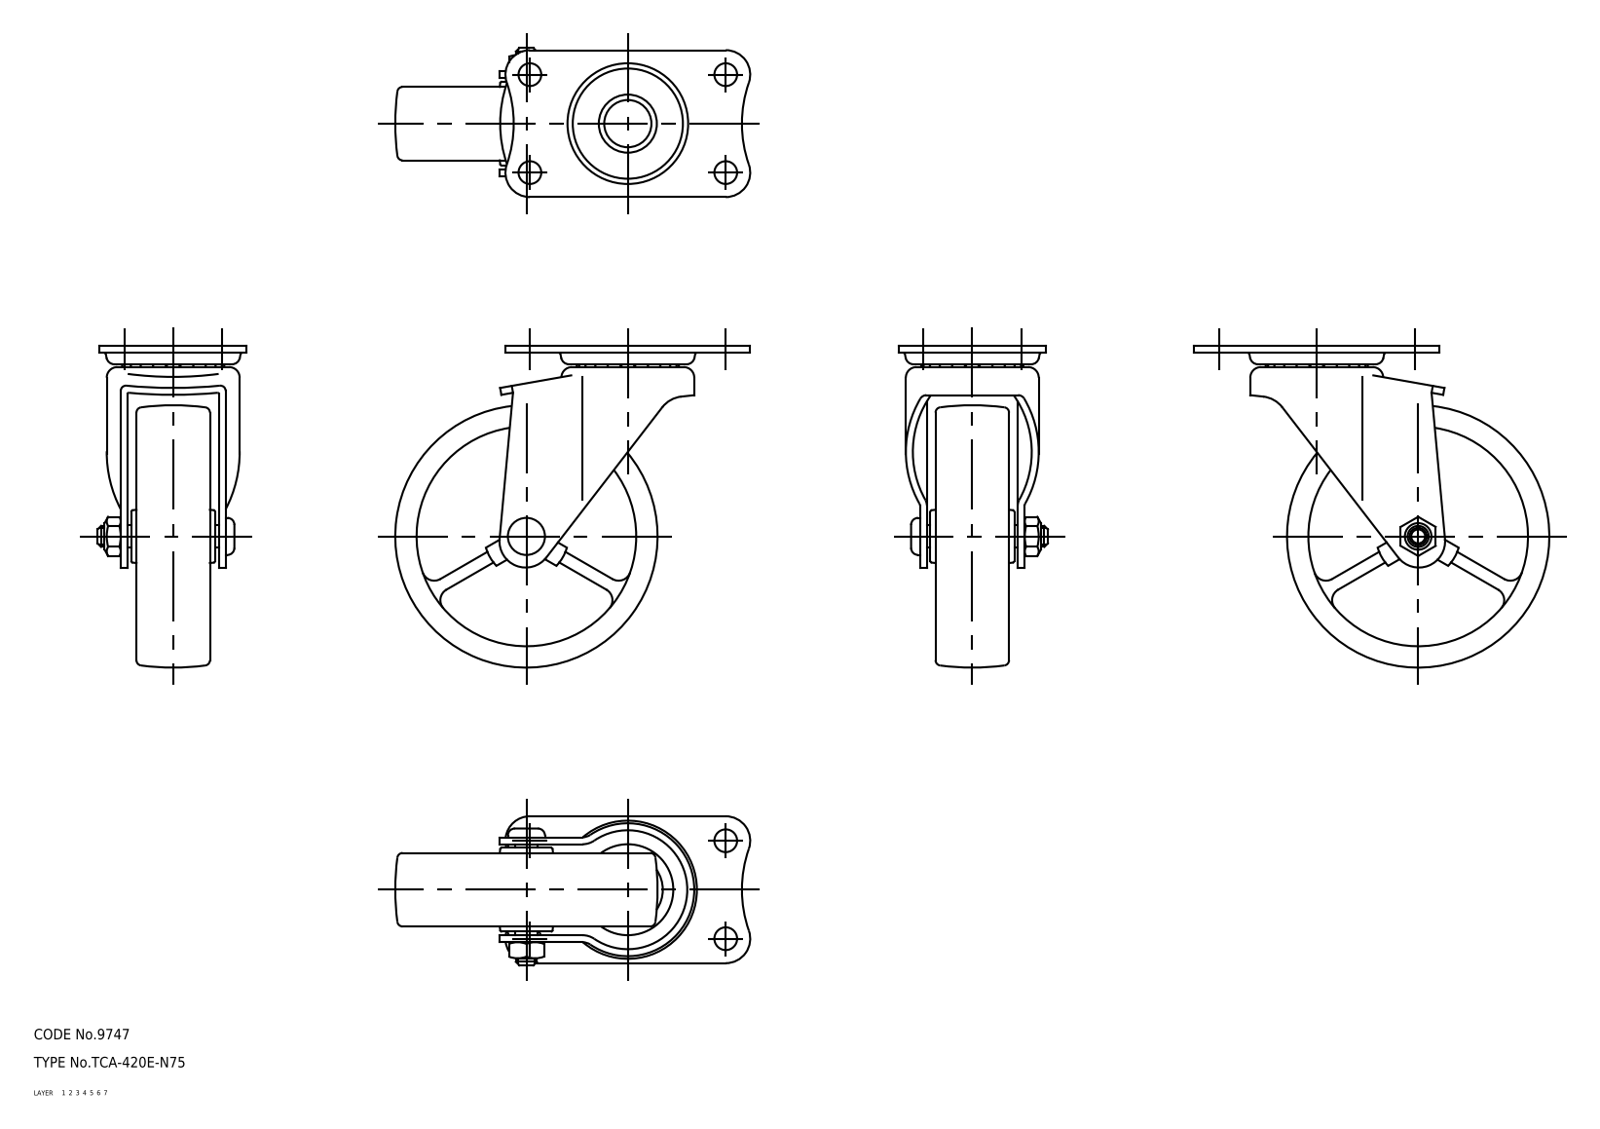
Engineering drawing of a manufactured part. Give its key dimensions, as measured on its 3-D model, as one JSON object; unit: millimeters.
{"part_name": "wheel; mounting plate; main shaft; axle (+1 more)", "step_written_by": "CADfix (AUTOMOTIVE_DESIGN)", "units": "millimeters", "bodies": {"solids": 5, "faces": 416, "planar": 0, "cylindrical": 0, "other": 416}, "overall_size": [101.5, 92, 42.6], "volume_mm3": 87555, "surface_area_mm2": 36787}
